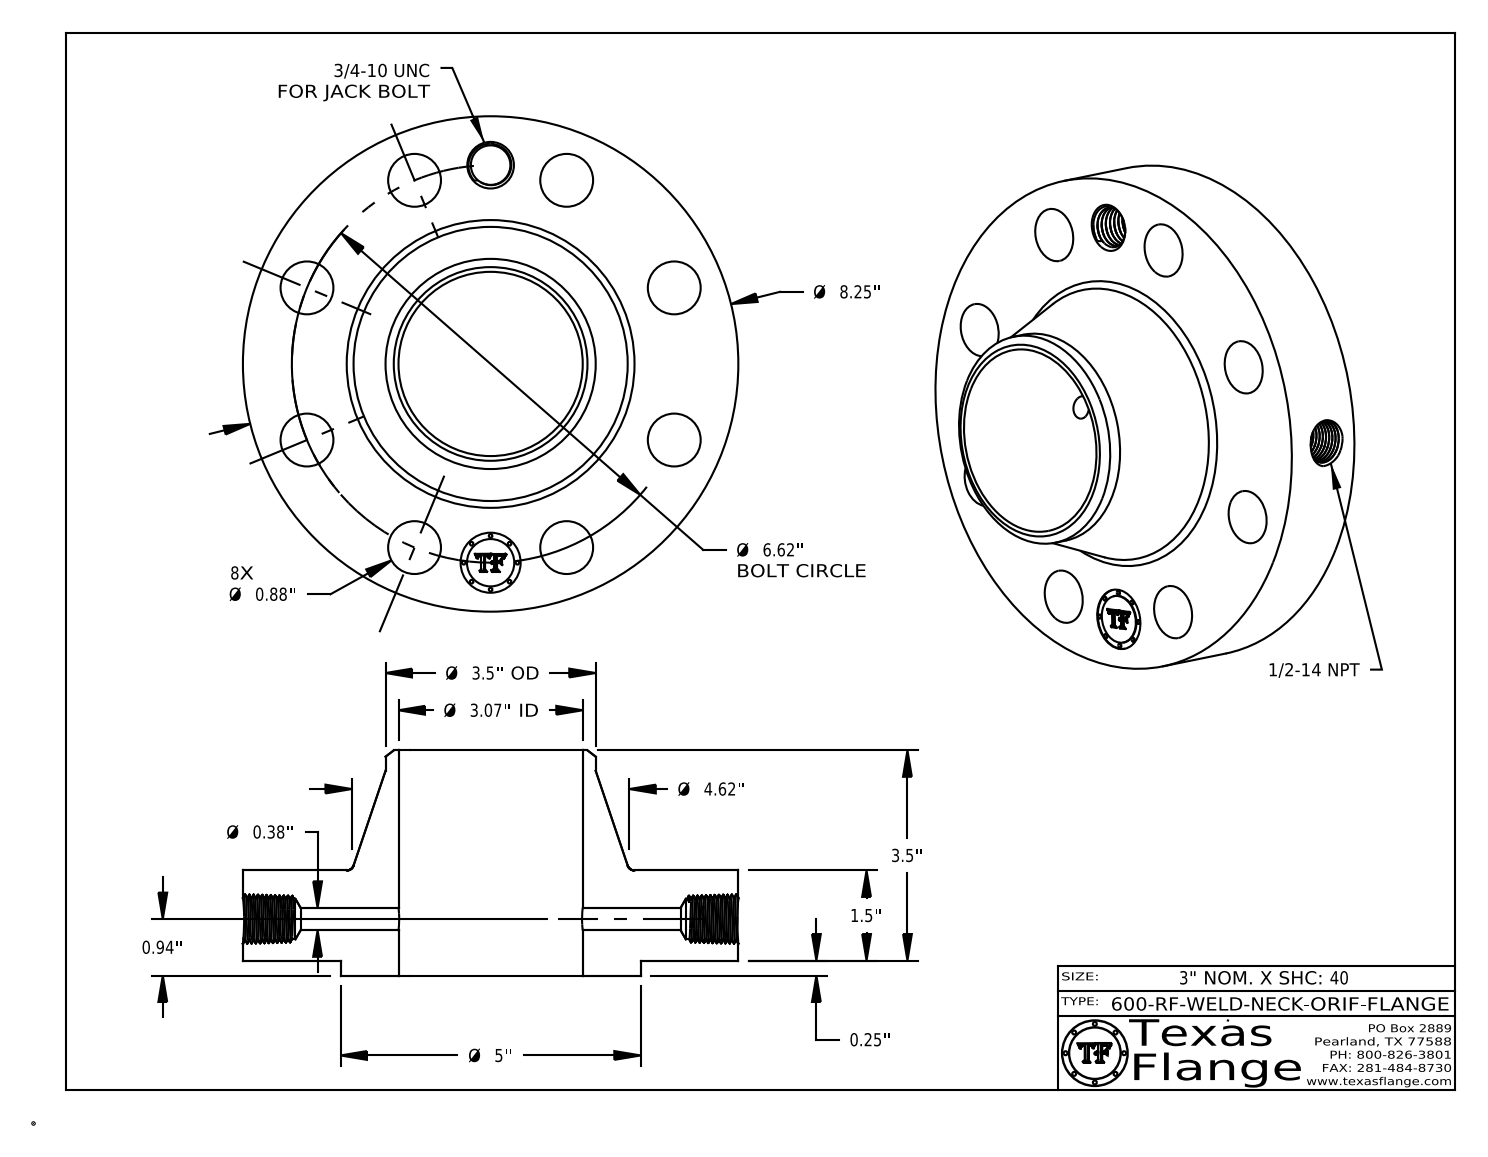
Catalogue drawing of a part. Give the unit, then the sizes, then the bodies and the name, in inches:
Units: inches
Overall size (bounding box): 8.25 × 8.25 × 3.75
Round holes (diameter × count): ⌀0.88 ×8, ⌀0.375 ×1, ⌀0.656 ×1, ⌀0.672 ×1, ⌀1 ×1, ⌀3.068 ×1
Round bosses / shafts (diameter × count): ⌀0.061 ×8, ⌀8.25 ×1, ⌀5 ×1, ⌀3.5 ×1, ⌀0.788 ×1
Main face-to-face distances: 1.5, 0.25, 1.75, 3.75, 3.5, 2, 0.015, 1.735, 1.485, 2.015
Hole centre spacings: 3.31, 4.681, 6.116, 6.62, 1.291, 2.533, 2.533, 3.678
Volume: 73.18 in³ · Surface area: 226.7 in²
Bodies: 1 solid, 769 faces (369 planar, 92 cylindrical, 308 other)
Part name (STEP PRODUCT): 600-RF-WELD-NECK
STEP written by: CATIA V5 STEP AP214 (AUTOMOTIVE_DESIGN)
